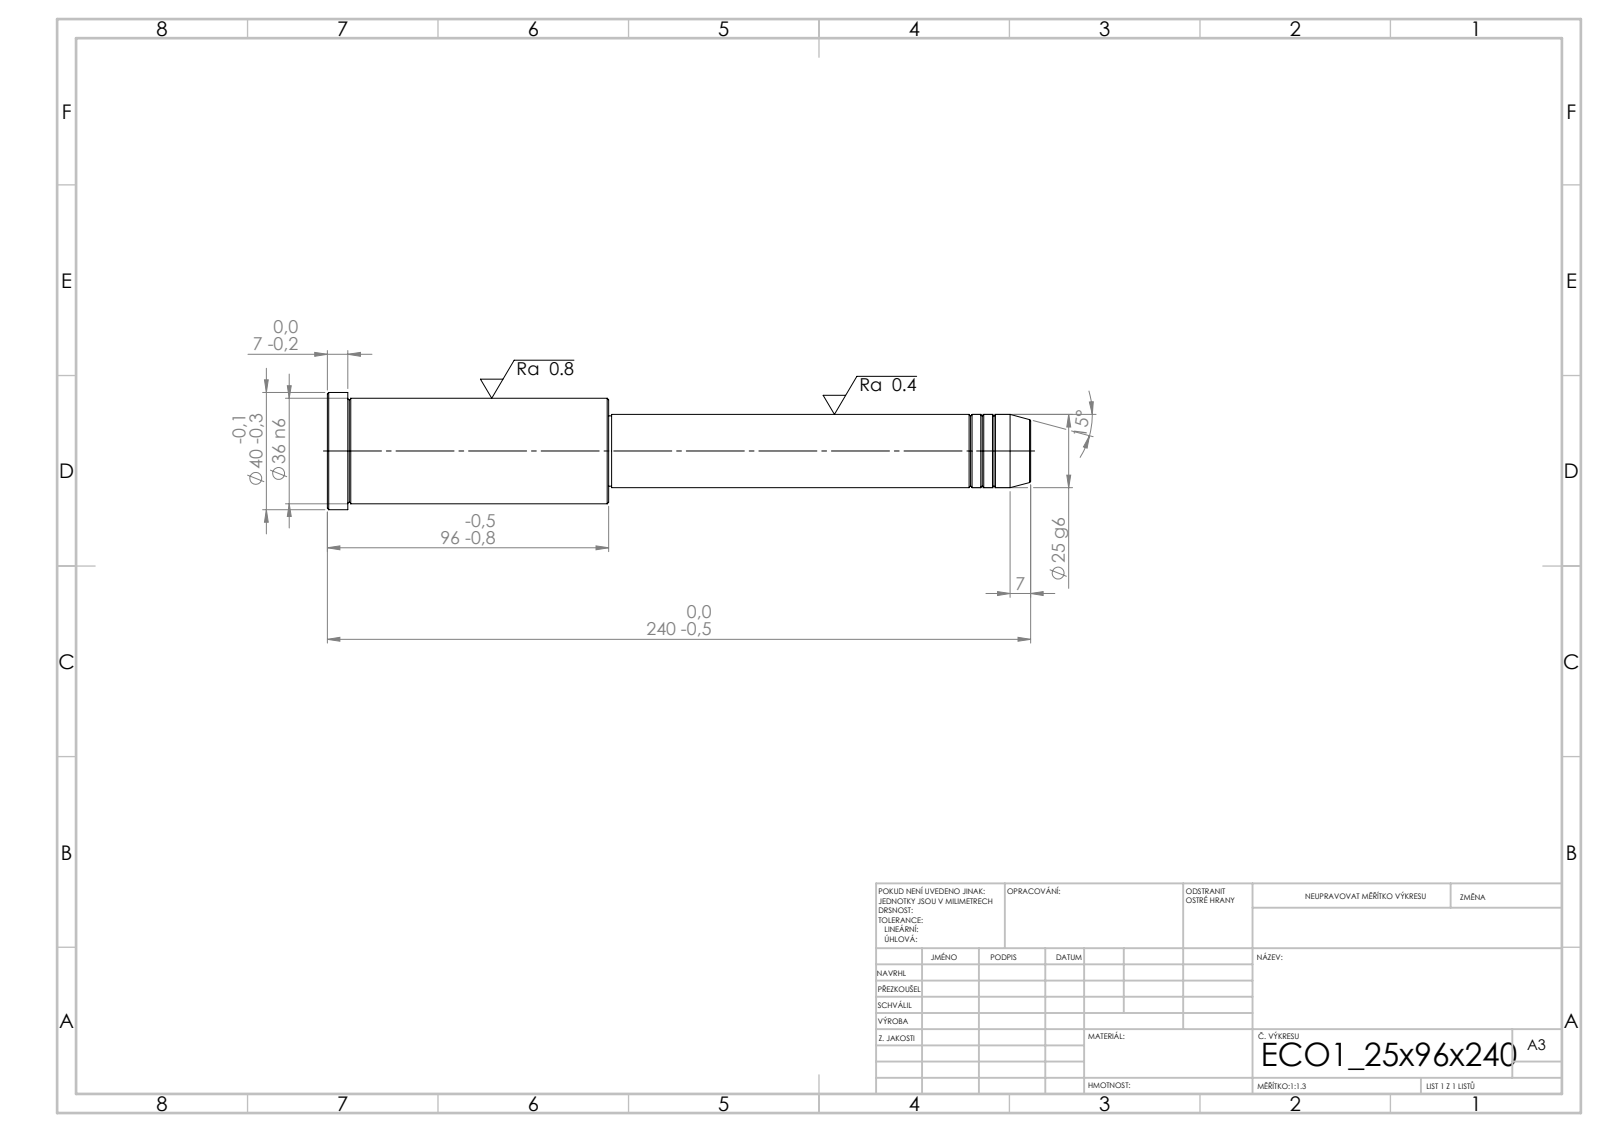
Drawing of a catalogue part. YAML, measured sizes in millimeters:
step_written_by: "SolidWorks 2019 (CONFIG_CONTROL_DESIGN)"
units: millimeters
bodies: {solids: 1, faces: 43, planar: 5, cylindrical: 14, other: 24}
overall_size: [240, 40, 40]
volume: 169379
surface_area: 24791
round_bosses_or_shafts:
  - {diameter: 40, count: 1}
  - {diameter: 36, count: 1}
  - {diameter: 25, count: 1}
  - {diameter: 24, count: 1}
face_to_face_distances: [96, 144, 240, 233, 89, 7, 143, 1, 90, 97]
